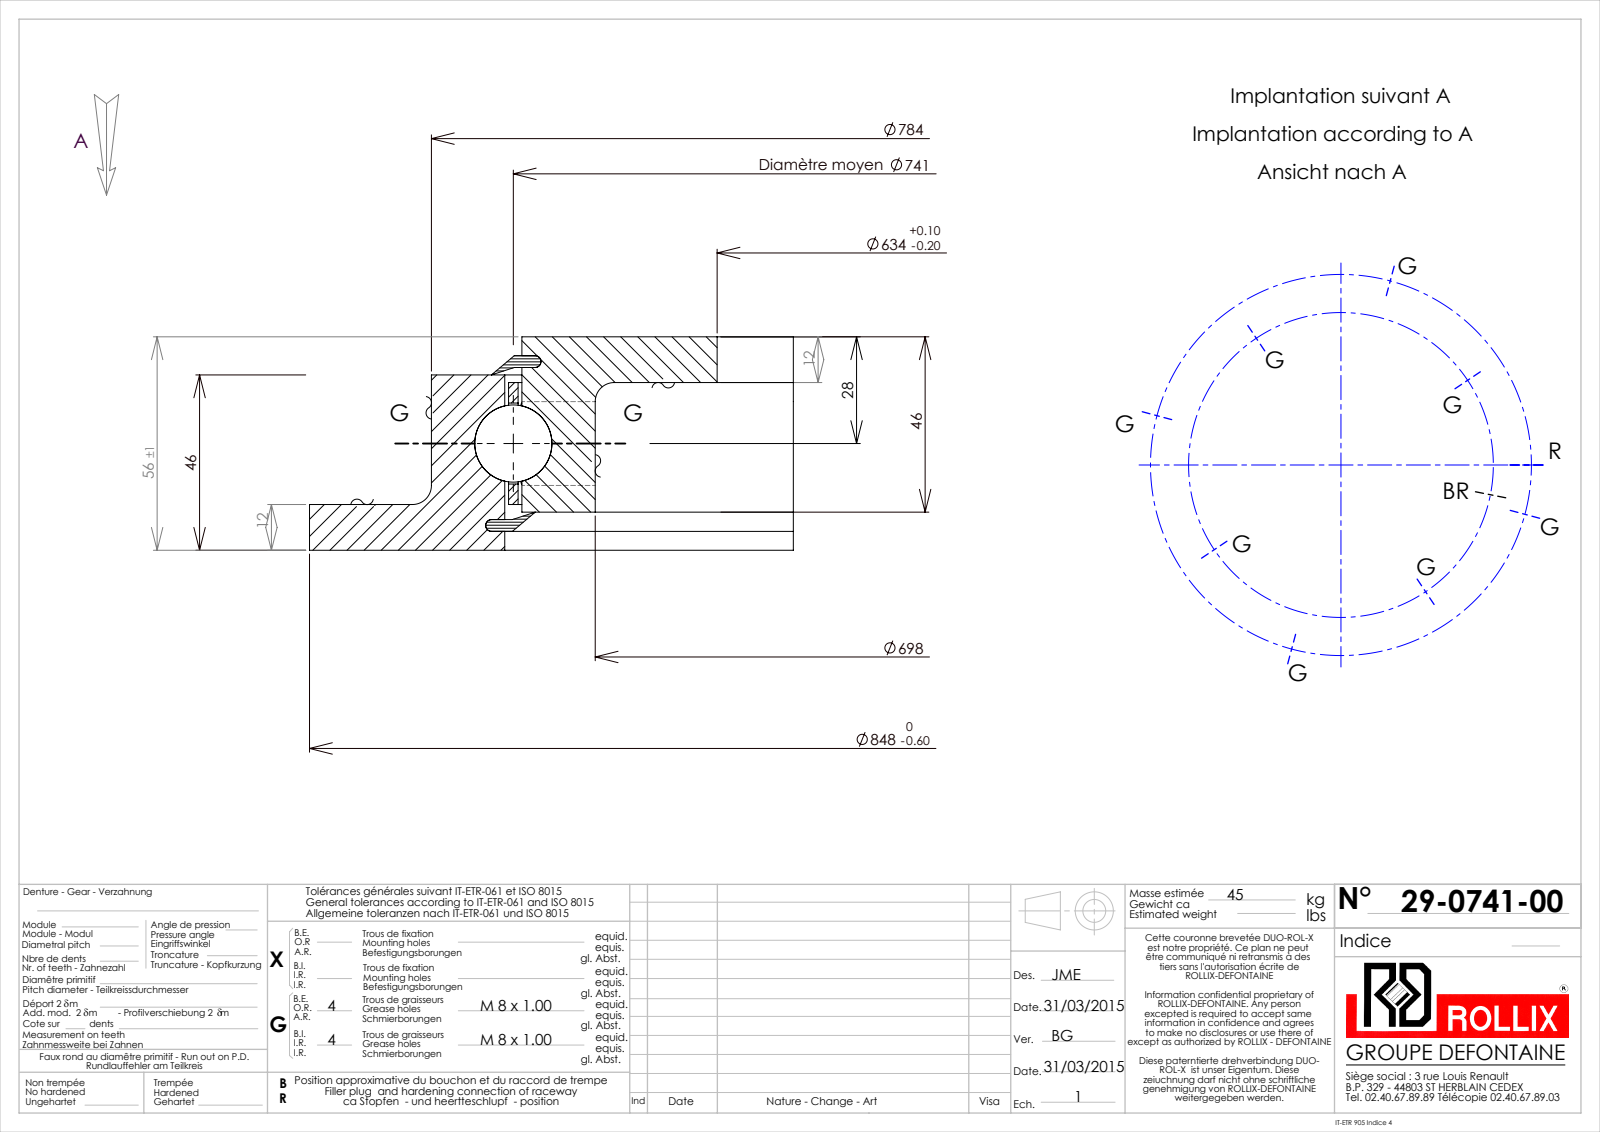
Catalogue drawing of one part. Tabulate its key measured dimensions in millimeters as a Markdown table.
| quantity | value |
| --- | --- |
| part name | 23-0741-00 |
| STEP written by | SolidWorks 2016 (CONFIG_CONTROL_DESIGN) |
| units | millimeters |
| bodies | 13 solids, 258 faces (94 planar, 52 cylindrical, 112 other) |
| overall size | 848 × 848 × 56 |
| volume | 5 520 000 mm³ |
| surface area | 1 115 000 mm² |
| round holes (diameter × count) | 7 × 8, 634 × 1, 698 × 1, 745.5 × 1 |
| round bosses / shafts (diameter × count) | 8 × 8, 848 × 1, 784 × 1, 736.5 × 1 |
| main face-to-face distances | 12, 44, 56, 10, 46, 2, 34, 32, 36, 4.95 |
